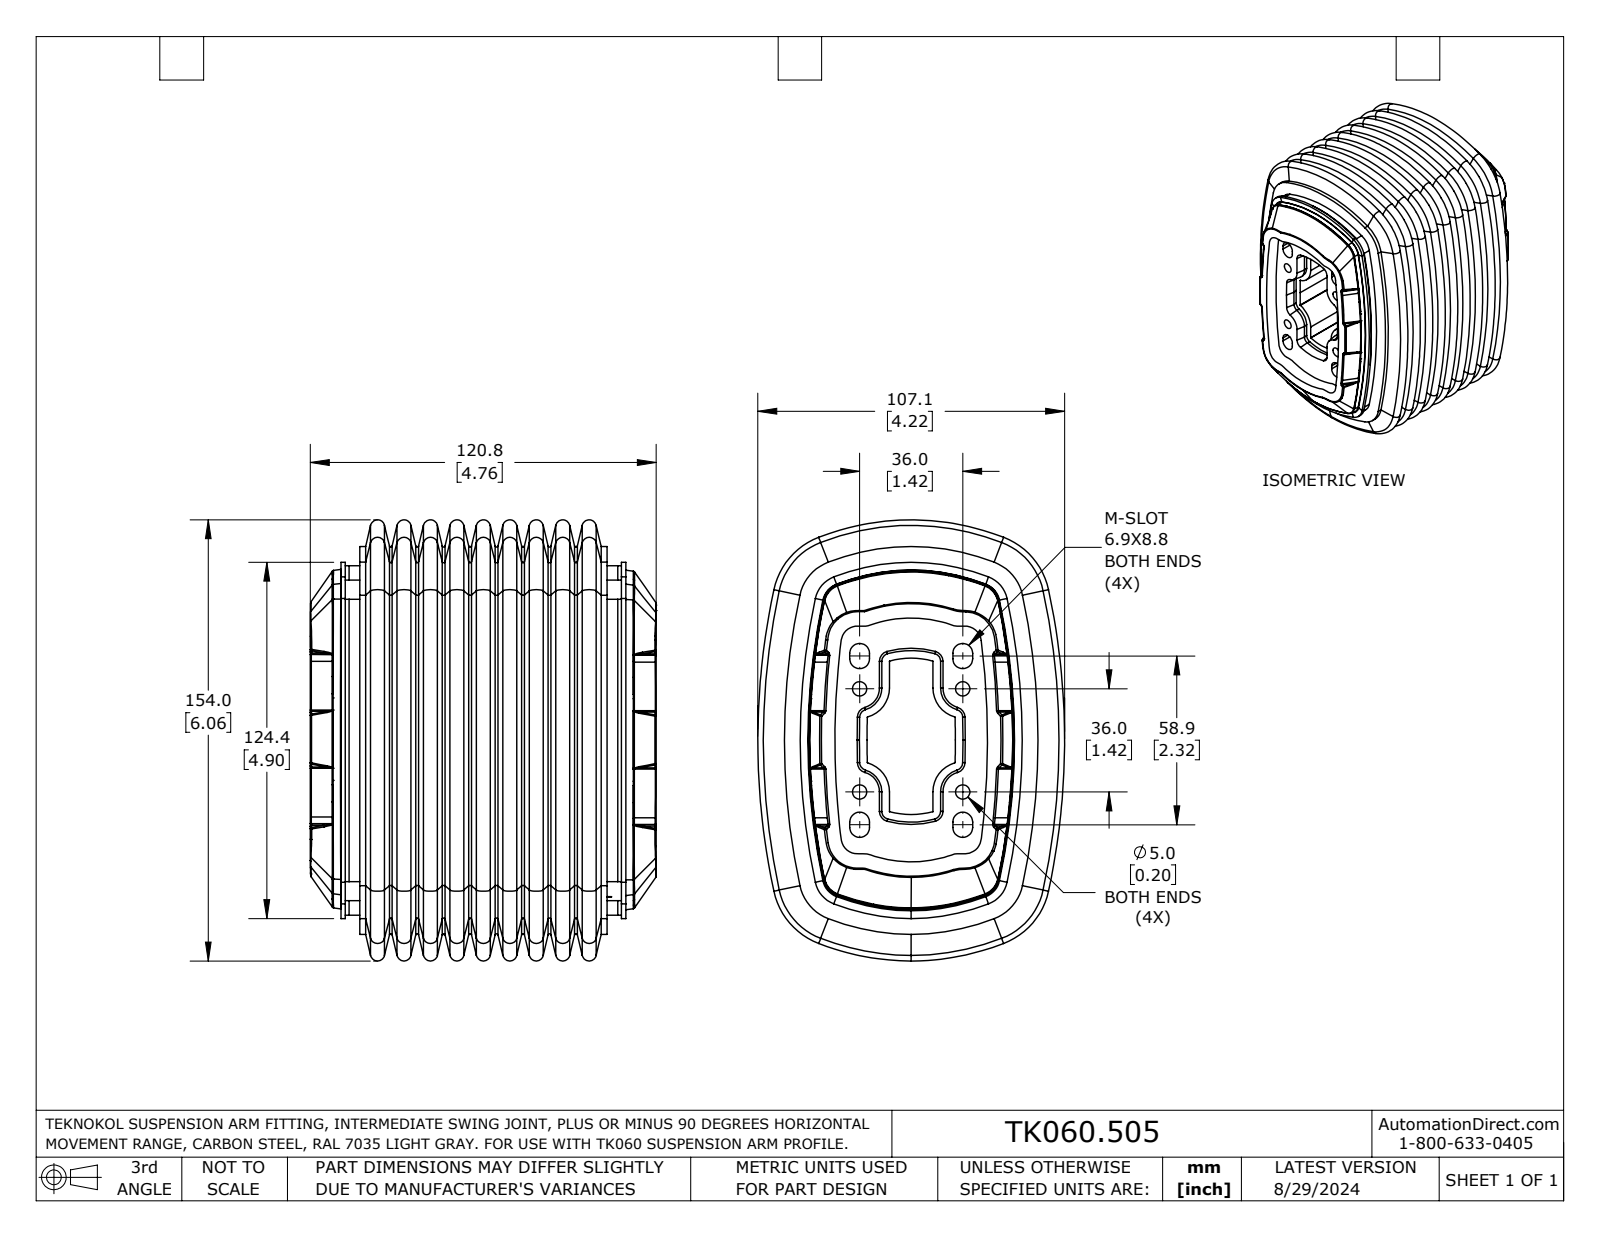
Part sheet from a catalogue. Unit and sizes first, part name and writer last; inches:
Units: inches
Overall size (bounding box): 6.063 × 4.756 × 4.218
Round holes (diameter × count): ⌀0.197 ×8
Partial cylindrical surfaces — rounded edges, fillets, slot ends (radius × count): R0.028 ×16, R0.136 ×16, R0.196 ×8, R0.107 ×4, R0.28 ×4, R0.302 ×4, R0.309 ×4, R0.361 ×4
Main face-to-face distances: 0.059, 3.34, 0.259, 3.598, 0.318, 3.657, 0.2, 3.539, 3.399, 3.281
Hole centre spacings: 1.417, 2.004
Volume: 53.09 in³ · Surface area: 405.5 in²
Bodies: 1 solid, 1374 faces (145 planar, 130 cylindrical, 1099 other)
Part name (STEP PRODUCT): TK060.505
STEP written by: SolidWorks 2023 (AUTOMOTIVE_DESIGN)
